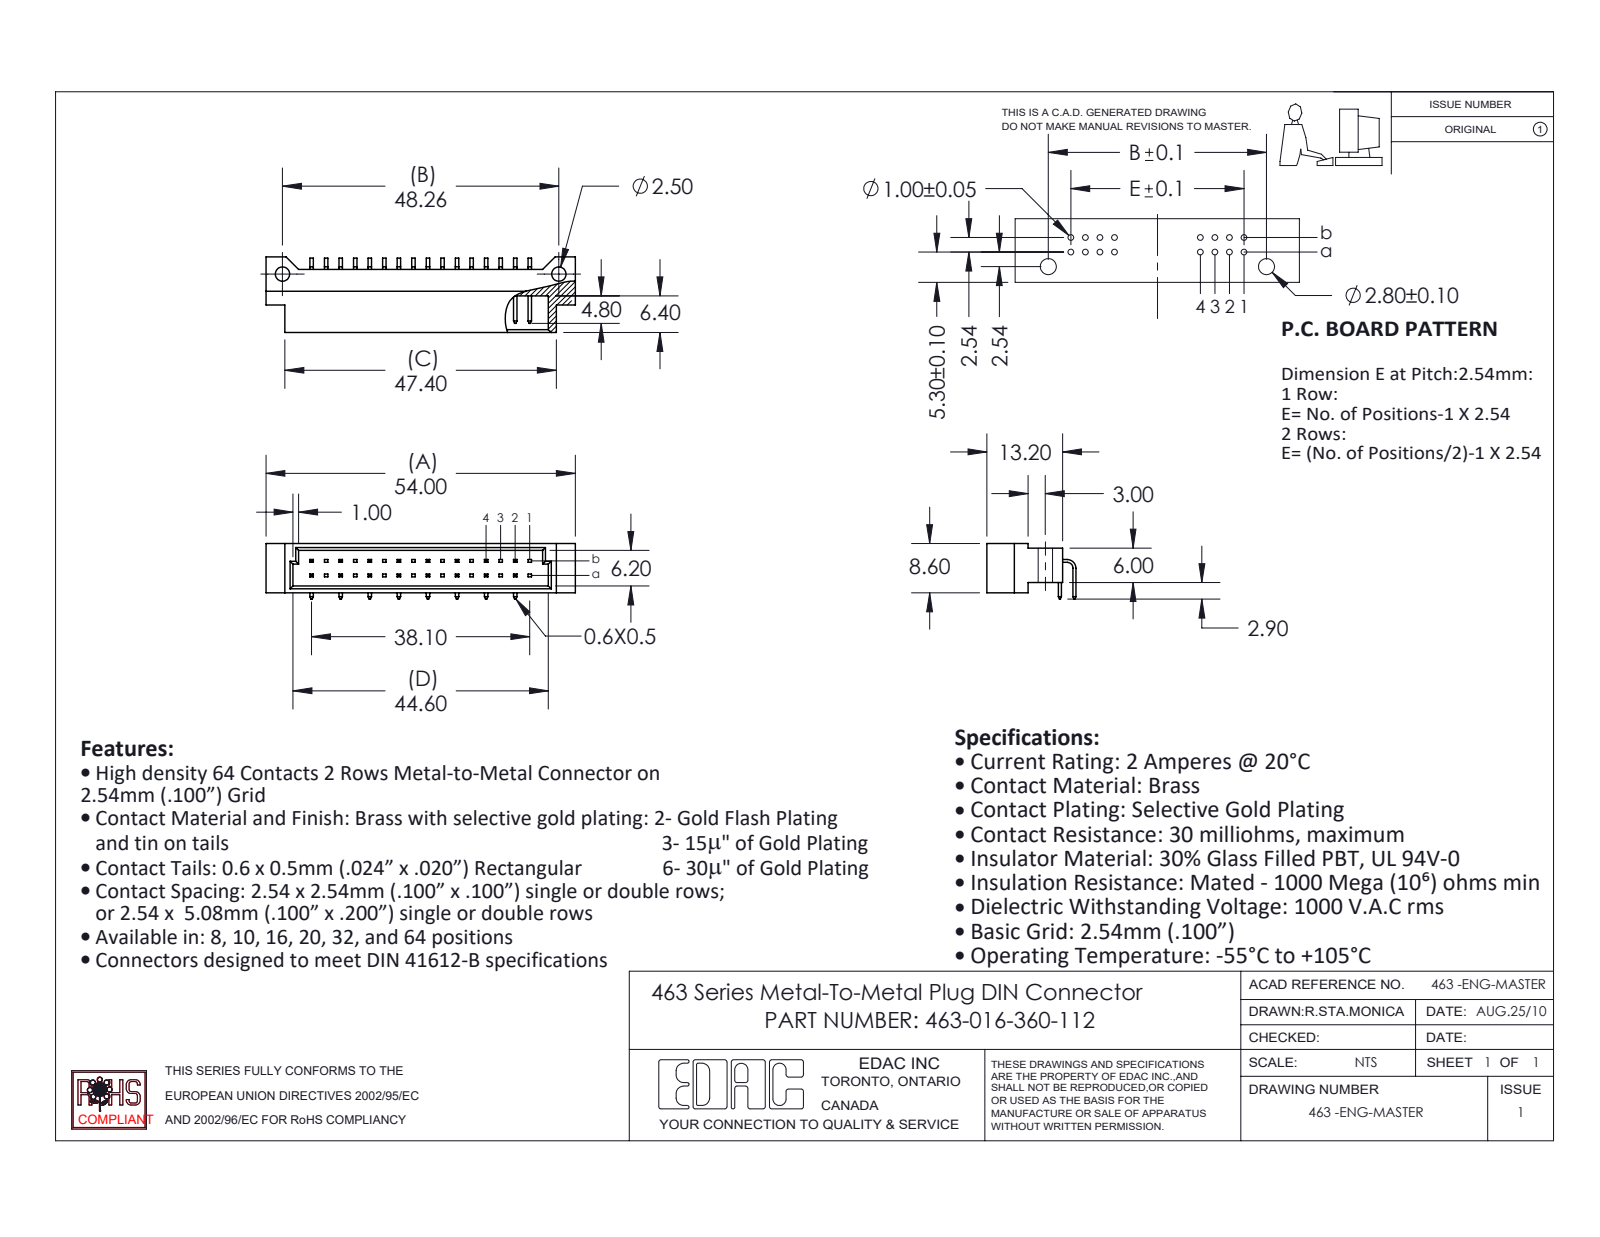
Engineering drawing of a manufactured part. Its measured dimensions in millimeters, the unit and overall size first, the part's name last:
Units: millimetres
Overall size (bounding box): 54 × 13.2 × 9.7
Round holes (diameter × count): ⌀2.5 ×2
Partial cylindrical surfaces — rounded edges, fillets, slot ends (radius × count): R1.02 ×1, R1.52 ×1
Main face-to-face distances: 1.2, 7.4, 8.6, 0.8, 6.2, 6, 6.8, 4.6, 5.6, 7.8
Hole centre spacings: 48.26
Volume: 2 638 mm³ · Surface area: 3 812 mm²
Bodies: 17 solids, 455 faces (419 planar, 36 cylindrical, 0 other)
Part name (STEP PRODUCT): 463-016-360-112; 463-290-1; 463 Part_32
STEP written by: SolidWorks 2020 (CONFIG_CONTROL_DESIGN)
